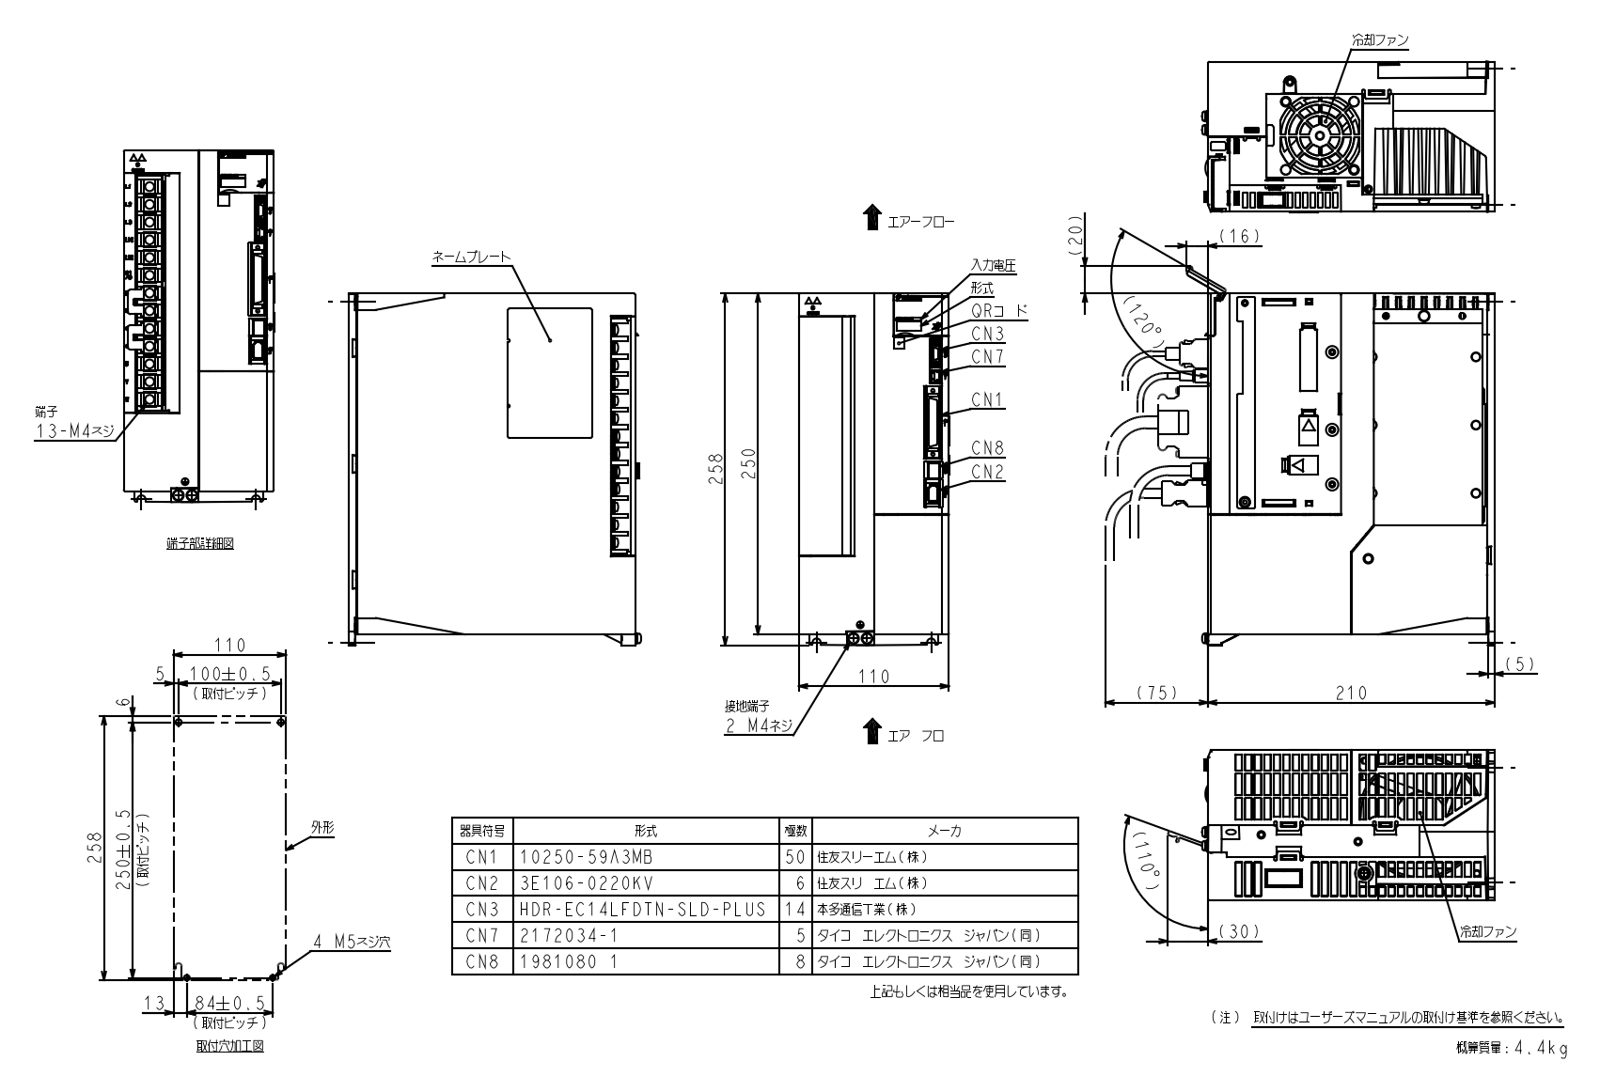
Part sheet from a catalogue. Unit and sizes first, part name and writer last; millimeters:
Units: millimetres
Overall size (bounding box): 258 × 214.6 × 110.5
Round holes (diameter × count): ⌀3 ×6, ⌀7 ×5, ⌀7.02 ×5, ⌀0.7 ×4, ⌀4 ×4, ⌀9 ×4, ⌀2.5 ×2, ⌀4.5 ×2, ⌀6 ×2, ⌀2.1 ×1, ⌀29.2 ×1, ⌀45.6 ×1
Round bosses / shafts (diameter × count): ⌀8 ×16, ⌀7.6 ×16, ⌀1.5 ×16, ⌀5.5 ×5, ⌀4 ×4, ⌀3.3 ×4, ⌀6.5 ×3, ⌀6 ×3
Partial cylindrical surfaces — rounded edges, fillets, slot ends (radius × count): R0.6 ×16, R2.5 ×6, R3 ×5, R0.5 ×4, R1 ×4, R13 ×4, R3.25 ×3, R4 ×2
Main face-to-face distances: 110, 209.5, 5.5, 2, 250, 104.5, 0.5, 248, 0.35, 109.65
Hole centre spacings: 35.36, 50, 5.5, 11, 70.71, 6.95, 12.18, 14.02
Volume: 5 481 000 mm³ · Surface area: 293 192 mm²
Bodies: 8 solids, 1968 faces (1731 planar, 234 cylindrical, 3 other)
Part name (STEP PRODUCT): SGD7S-330A00A; SGD7S-330A00A_PART1; SGD7S-330A00A_PART2; SGD7S-330A00A_PART3 (+3 more)
STEP written by: PARTsolutions (AUTOMOTIVE_DESIGN)
